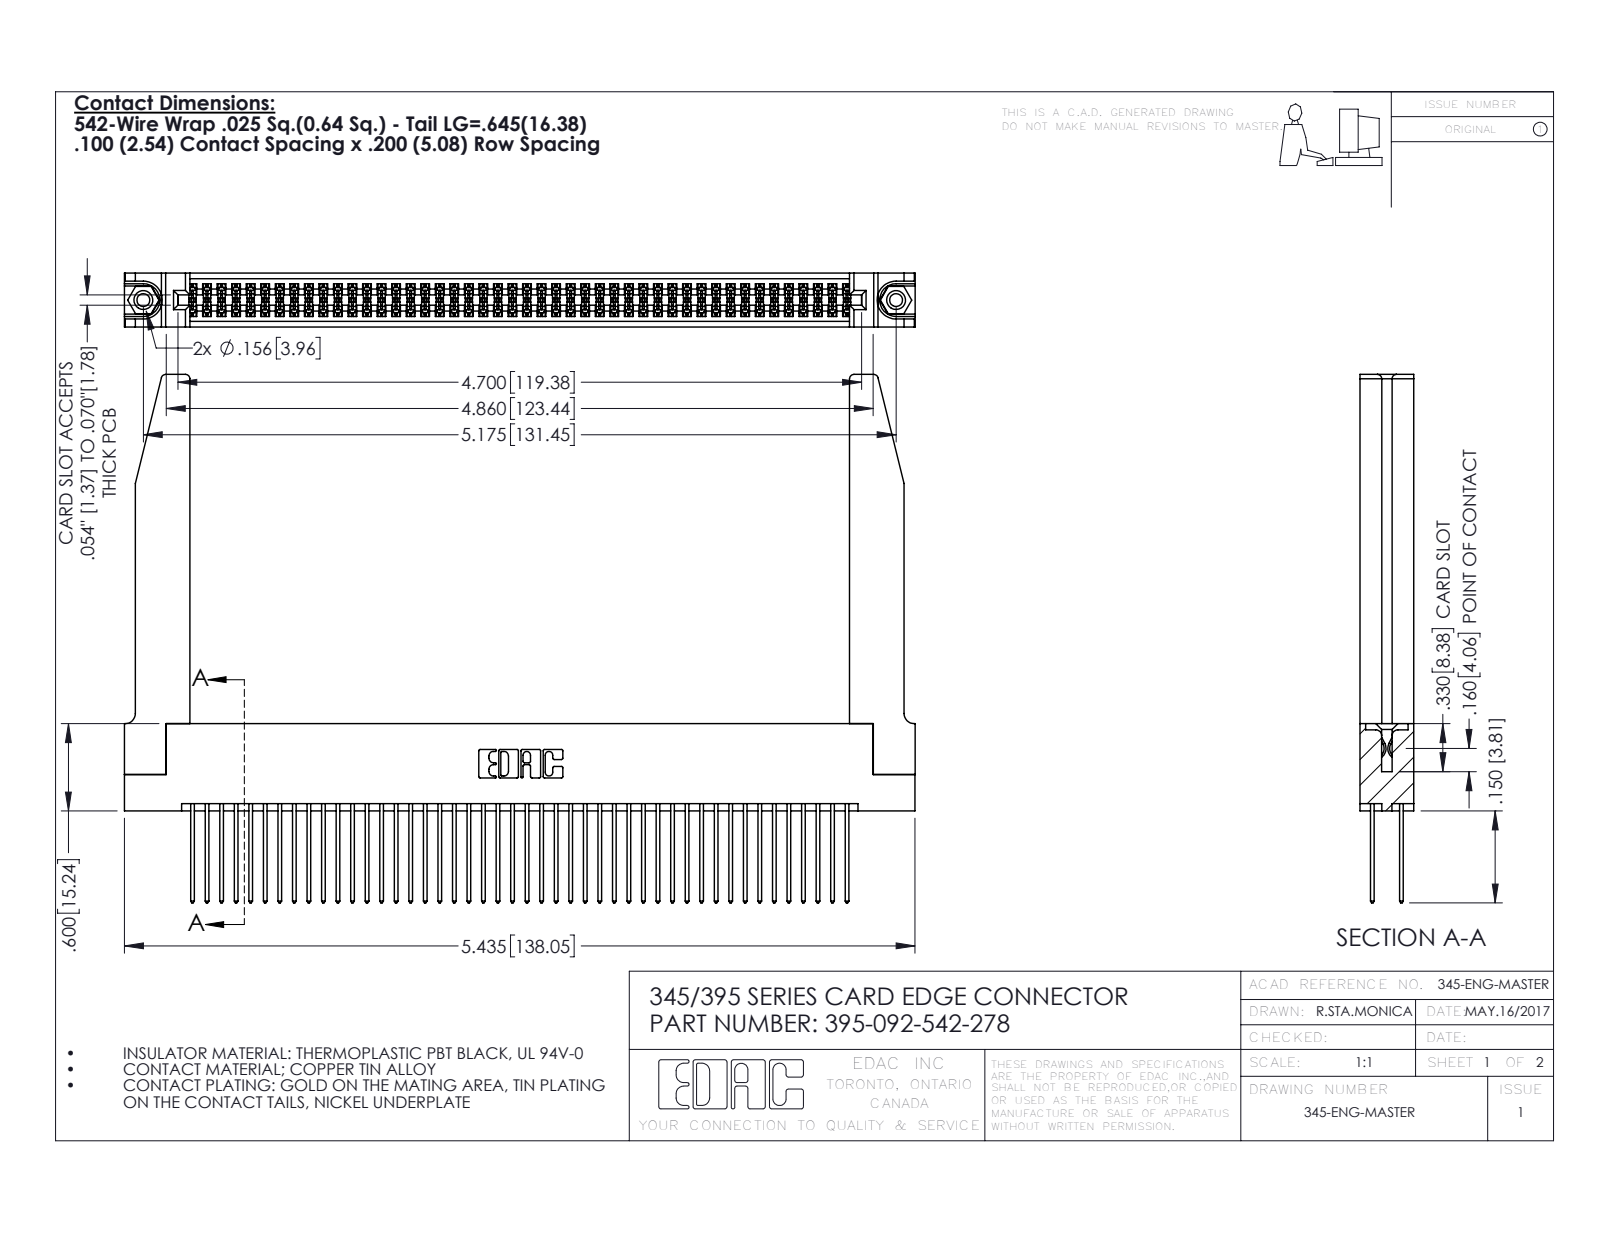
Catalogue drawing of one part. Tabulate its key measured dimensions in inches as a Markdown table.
| quantity | value |
| --- | --- |
| part name | 345-220-078_345-220-078; 345-292-001_345-293-142; 395-092-542-278; 345-250-001_345-250-001-102 (+1 more) |
| STEP written by | SolidWorks 2016 (CONFIG_CONTROL_DESIGN) |
| units | inches |
| bodies | 97 solids, 4960 faces (3258 planar, 1650 cylindrical, 52 other) |
| overall size | 5.436 × 3.632 × 0.37 |
| volume | 1.321 in³ |
| surface area | 45.62 in² |
| round holes (diameter × count) | 0.089 × 2, 0.125 × 2, 0.156 × 2, 0.064 × 1 |
| round bosses / shafts (diameter × count) | 0.155 × 2 |
| partial cylindrical surfaces (radius × count) | 0.006 × 138, 0.01 × 92, 0.01 × 22, 0.03 × 8, 0.007 × 6, 0.031 × 6, 0.026 × 3, 0.014 × 2 |
| main face-to-face distances | 0.072, 0.298, 0.37, 0.2, 0.098, 0.272, 0.025, 0.225, 0.175, 0.148 |
| hole center spacings | 0.27, 4.939, 5.175 |
